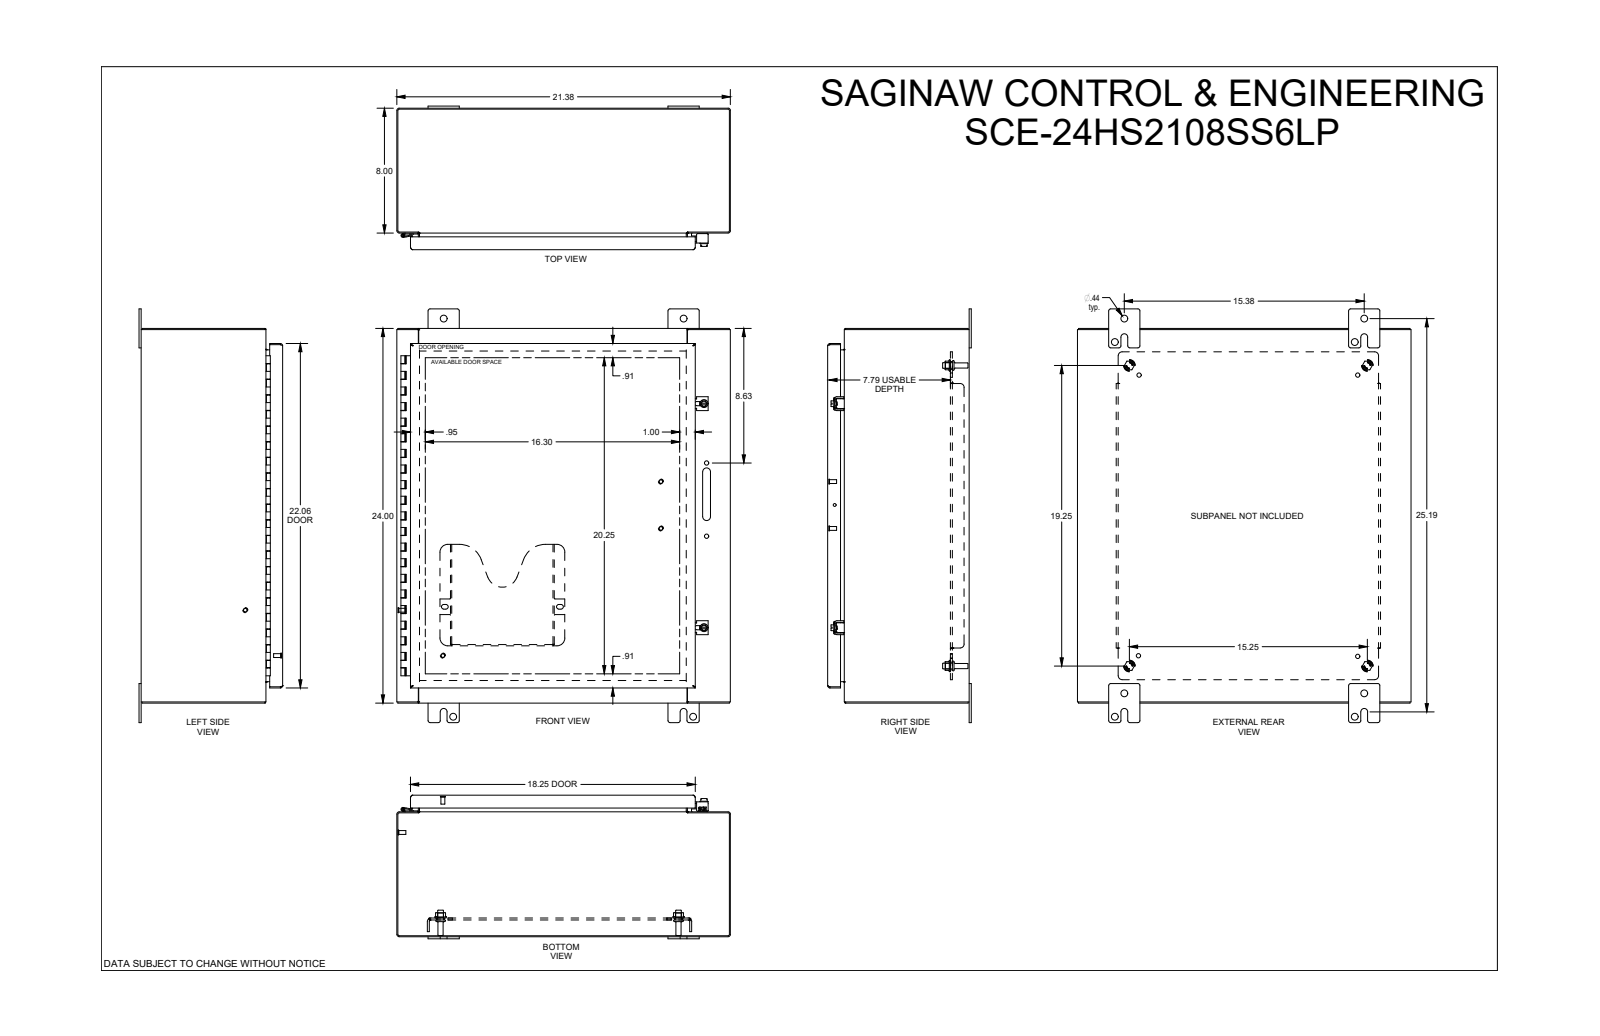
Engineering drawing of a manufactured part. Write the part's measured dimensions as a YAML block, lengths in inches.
part_name: "SCE-24HS2108LP"
step_written_by: "SolidWorks 2021 (AUTOMOTIVE_DESIGN)"
units: inches
bodies: {solids: 53, faces: 2771, planar: 1028, cylindrical: 881, other: 862}
overall_size: [26.5, 21.375, 9.343]
volume: 206.2
surface_area: 4882
round_holes:
  - {diameter: 0.281, count: 6}
  - {diameter: 0.172, count: 4}
  - {diameter: 0.205, count: 4}
  - {diameter: 0.244, count: 4}
  - {diameter: 0.31, count: 4}
  - {diameter: 0.312, count: 4}
  - {diameter: 0.367, count: 4}
  - {diameter: 0.375, count: 4}
  - {diameter: 0.5, count: 4}
  - {diameter: 0.04, count: 2}
  - {diameter: 0.203, count: 2}
  - {diameter: 0.218, count: 2}
round_bosses_or_shafts:
  - {diameter: 0.248, count: 8}
  - {diameter: 0.25, count: 6}
  - {diameter: 0.59, count: 4}
  - {diameter: 0.376, count: 4}
  - {diameter: 0.366, count: 4}
  - {diameter: 0.332, count: 4}
  - {diameter: 0.24, count: 4}
  - {diameter: 0.17, count: 4}
partial_cylinders:
  - {radius: 0.01, count: 107}
  - {radius: 0.025, count: 104}
  - {radius: 0.062, count: 32}
  - {radius: 0.185, count: 21}
  - {radius: 0.015, count: 20}
  - {radius: 0.04, count: 18}
  - {radius: 0.043, count: 12}
  - {radius: 0.118, count: 12}
face_to_face_distances: [0.075, 8.993, 8.918, 9.068, 21.3, 0.125, 1.2, 1.125, 7.793, 7.868]
hole_center_spacings: [0.875, 15.375, 18.641, 0.493, 0.494, 0.984, 1.375, 1.637]
